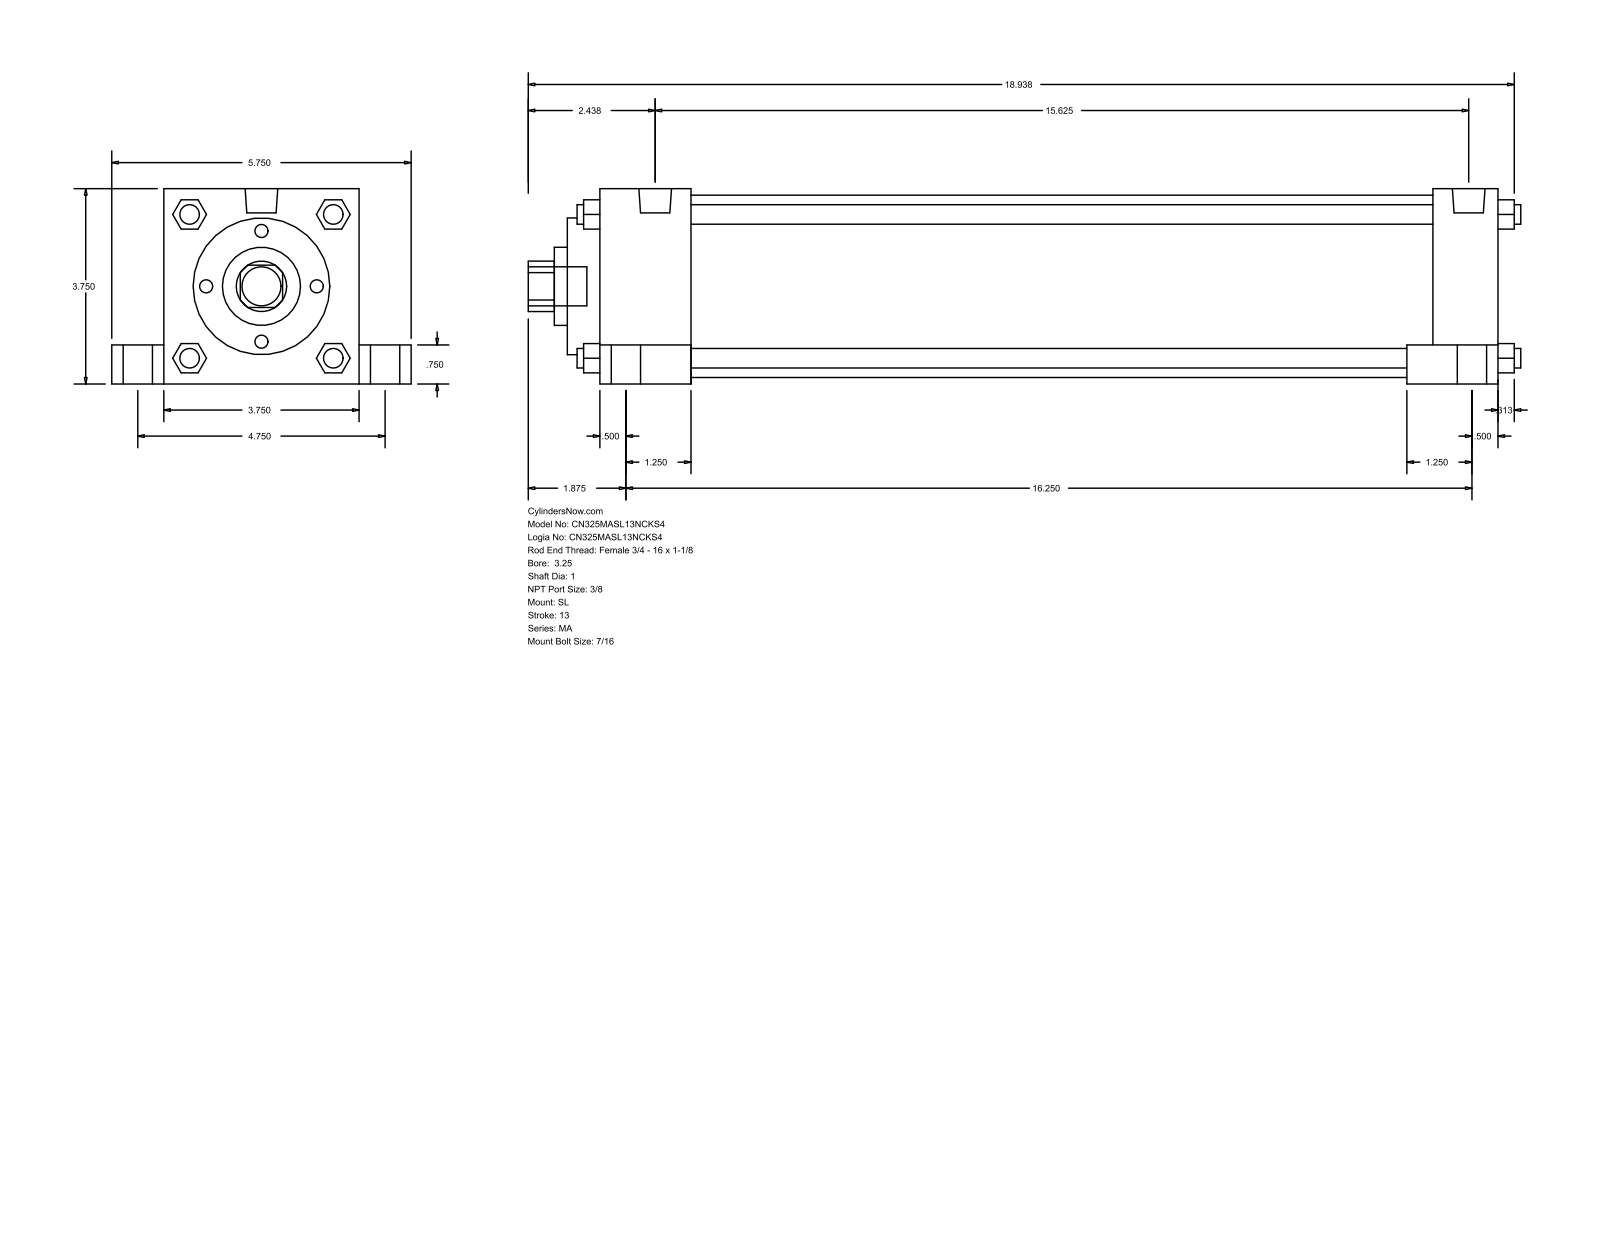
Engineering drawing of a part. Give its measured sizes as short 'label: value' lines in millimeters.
name: MA_SL__0325_1
written by: GSSL Pune (CONFIG_CONTROL_DESIGN)
unit: mm
bodies: 0 solids, 150 faces (113 planar, 37 cylindrical, 0 other)
size: 484.19 × 146.05 × 95.25
holes: 1× ⌀25.4, 1× ⌀38.1, 1× ⌀66.67, 1× ⌀88.9
bosses: 4× ⌀20.64, 4× ⌀14.29, 4× ⌀11.11, 4× ⌀9.53, 2× ⌀15.93, 1× ⌀19.05
rounds: 1× R12.29
face distances: 95.24, 438.15, 15.87, 25.41, 120.65, 454.02, 19.05, 406.4, 31.75, 44.46
